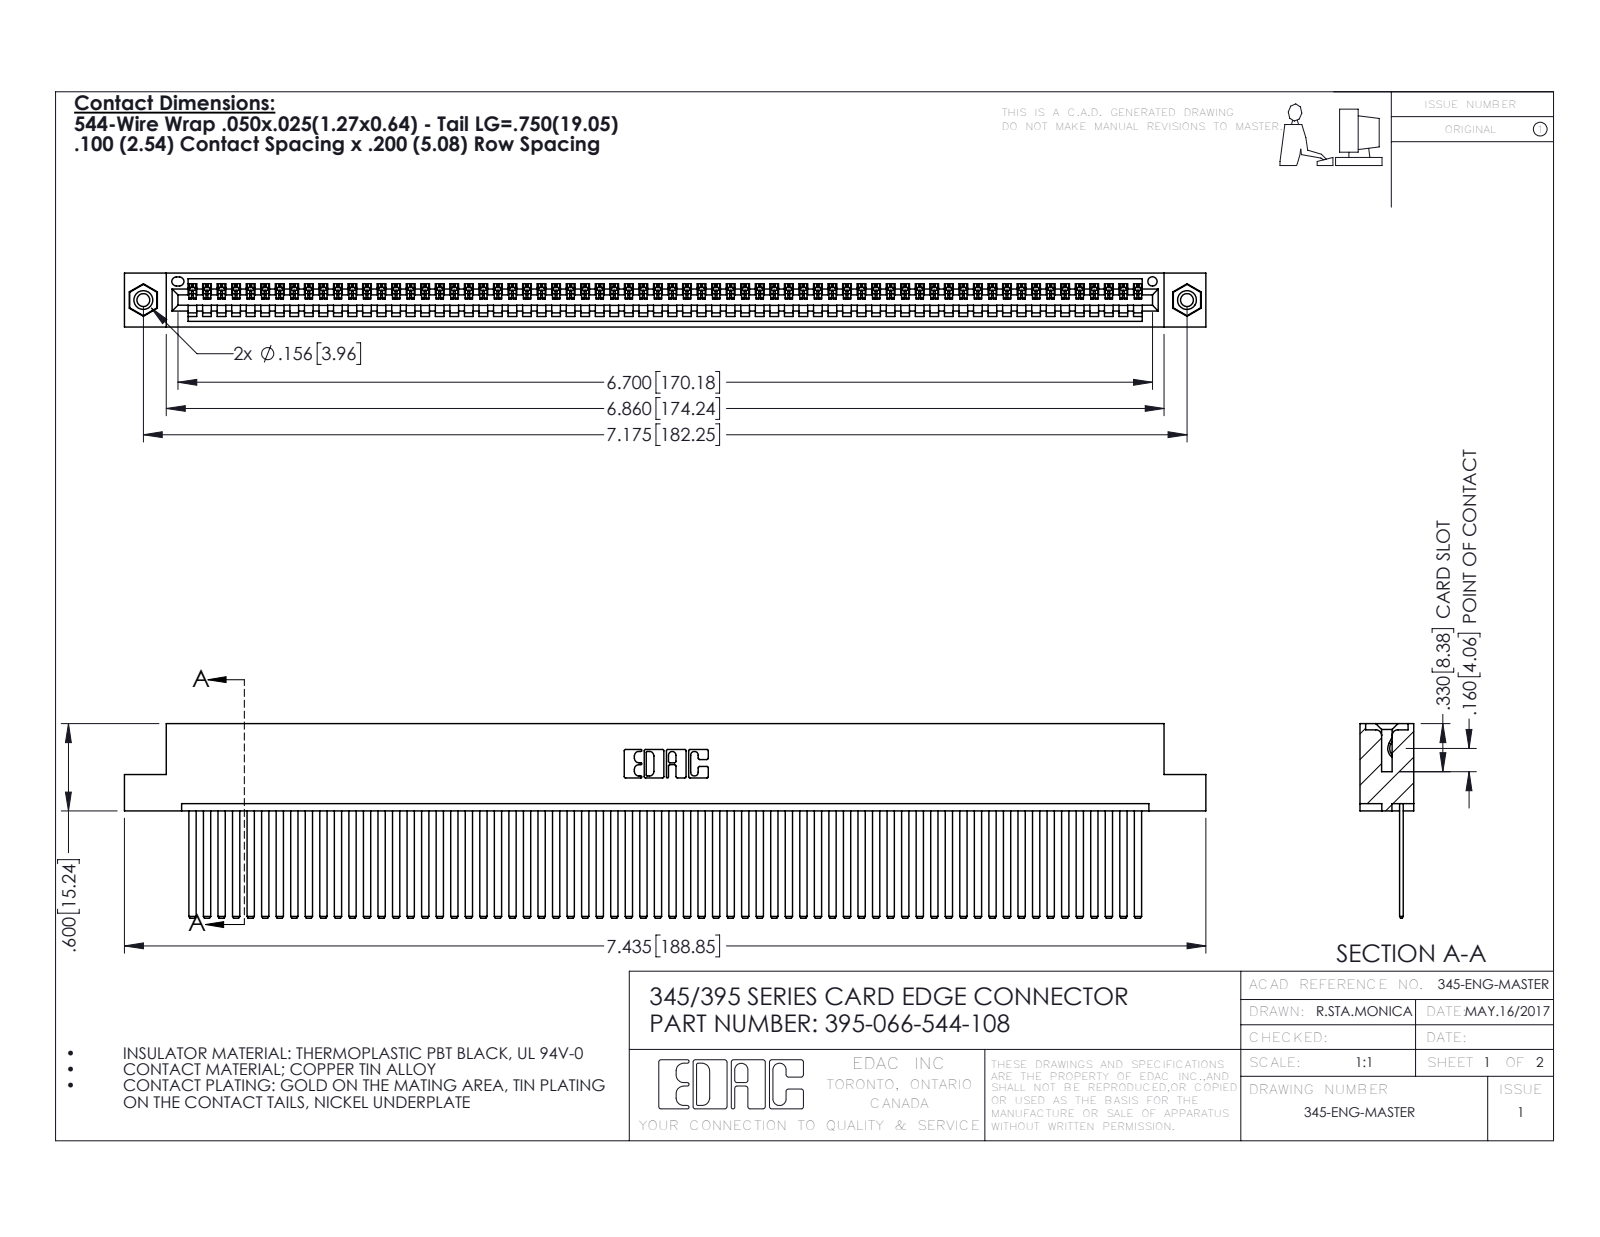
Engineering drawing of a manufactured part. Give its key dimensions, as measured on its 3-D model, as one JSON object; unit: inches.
{"part_name": "345 Part_Flush Mounting Lugs - 0.156 Dia-TI; 345-250-001_345-250-003-102; 395-066-544-108; 345-292-001_345-293-144", "step_written_by": "SolidWorks 2016 (CONFIG_CONTROL_DESIGN)", "units": "inches", "bodies": {"solids": 69, "faces": 3618, "planar": 2488, "cylindrical": 1114, "other": 16}, "overall_size": [7.435, 1.337, 0.37], "volume_in3": 1.153, "surface_area_in2": 43.01, "round_holes": [[0.089, 2], [0.125, 2], [0.156, 2], [0.064, 1]], "round_bosses_or_shafts": [[0.155, 2]], "partial_cylinders_radius": [[0.006, 132], [0.01, 22], [0.007, 6], [0.031, 6], [0.026, 3], [0.031, 2], [0.04, 2], [0.014, 1]], "face_to_face_distances": [0.072, 0.298, 0.025, 0.098, 0.272, 0.37, 0.2, 0.225, 0.149, 0.072], "hole_center_spacings": [0.27, 6.939, 7.175]}
